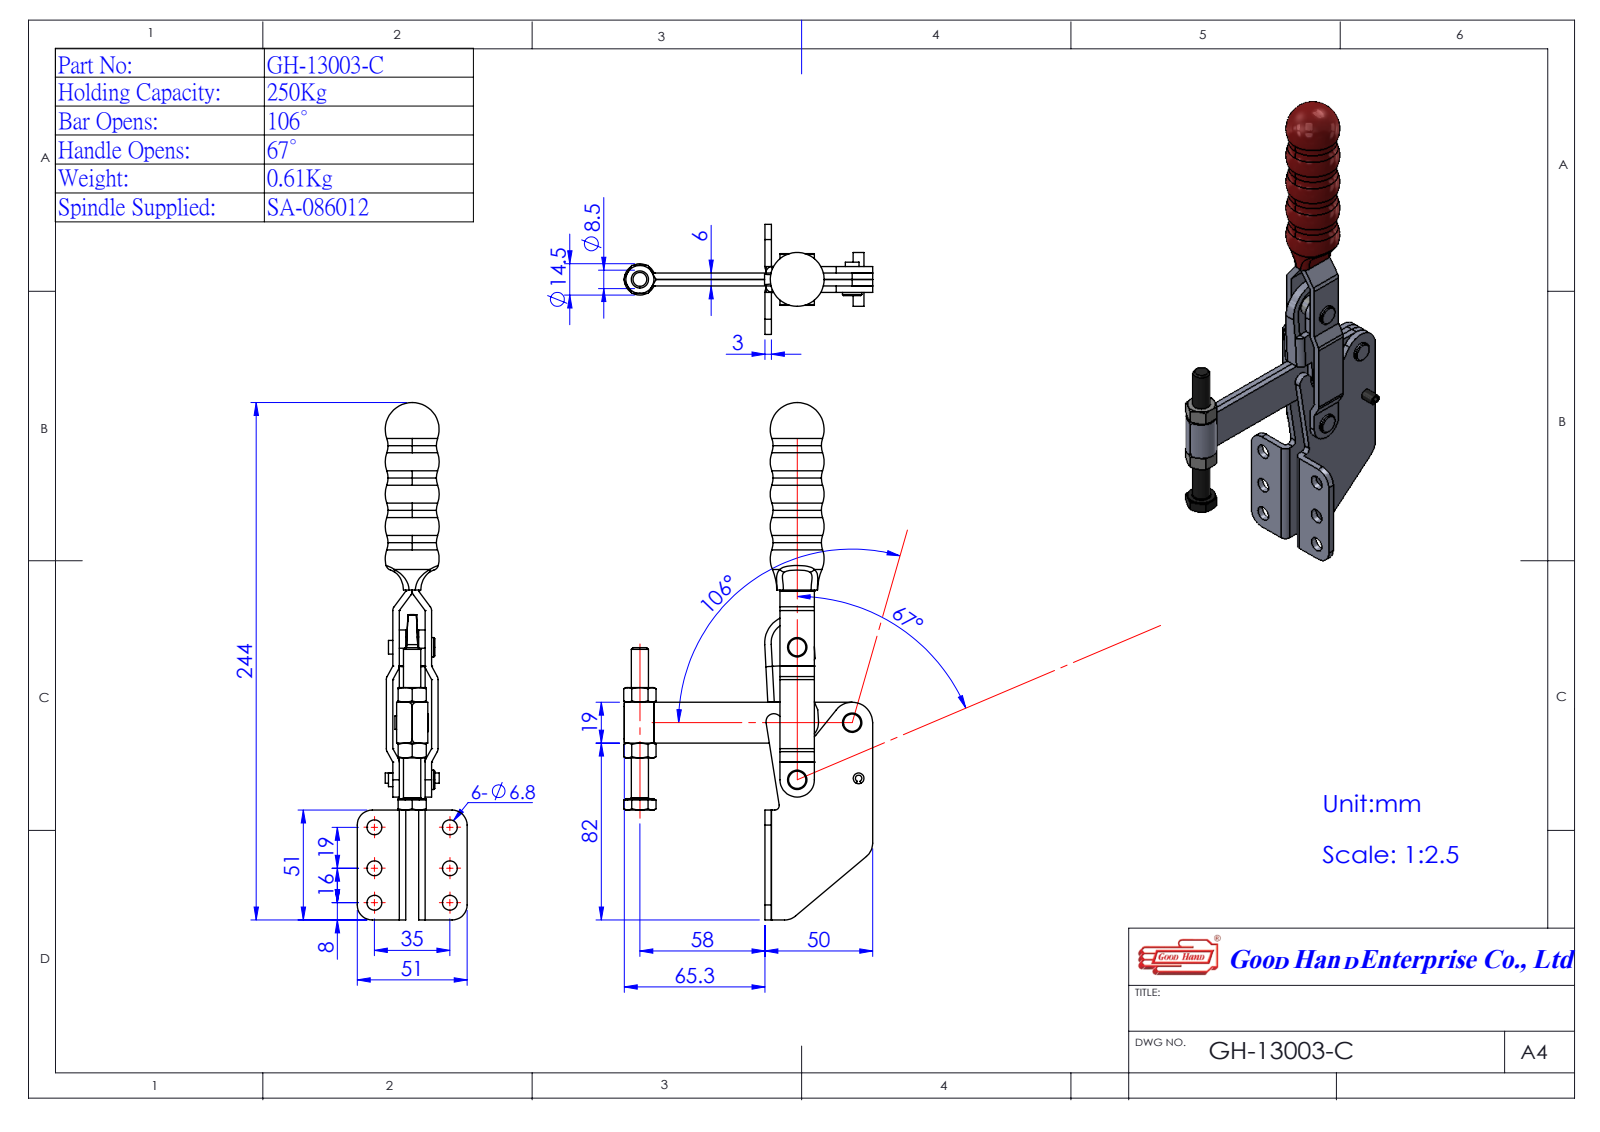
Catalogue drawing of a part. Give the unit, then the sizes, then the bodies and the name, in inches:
Units: inches
Overall size (bounding box): 9.606 × 4.537 × 2.008
Round holes (diameter × count): ⌀0.268 ×7, ⌀0.197 ×4, ⌀0.315 ×1, ⌀0.335 ×1
Round bosses / shafts (diameter × count): ⌀0.354 ×4, ⌀0.295 ×3, ⌀0.247 ×2, ⌀0.571 ×1, ⌀0.492 ×1, ⌀0.197 ×1
Partial cylindrical surfaces — rounded edges, fillets, slot ends (radius × count): R0.276 ×4, R0.315 ×3, R0.079 ×2, R0.119 ×2, R0.144 ×1, R0.354 ×1, R0.374 ×1, R1.181 ×1
Main face-to-face distances: 0.118, 0.354, 0.236, 0.472, 0.591, 0.709, 0.827, 0.748, 0.63, 0.059
Hole centre spacings: 1.378, 0.63, 0.748, 1.515, 1.568, 1.949, 0.932, 1.046
Volume: 6.685 in³ · Surface area: 80.37 in²
Bodies: 5 solids, 302 faces (126 planar, 108 cylindrical, 68 other)
Part name (STEP PRODUCT): Group3^GH-13003-C(簡化)-1; GH-13003-C(簡化)-1; 零件11^GH-13003-C(簡化)-1; Group1^GH-13003-C(簡化)-1 (+2 more)
STEP written by: SolidWorks 2016 (AUTOMOTIVE_DESIGN)
